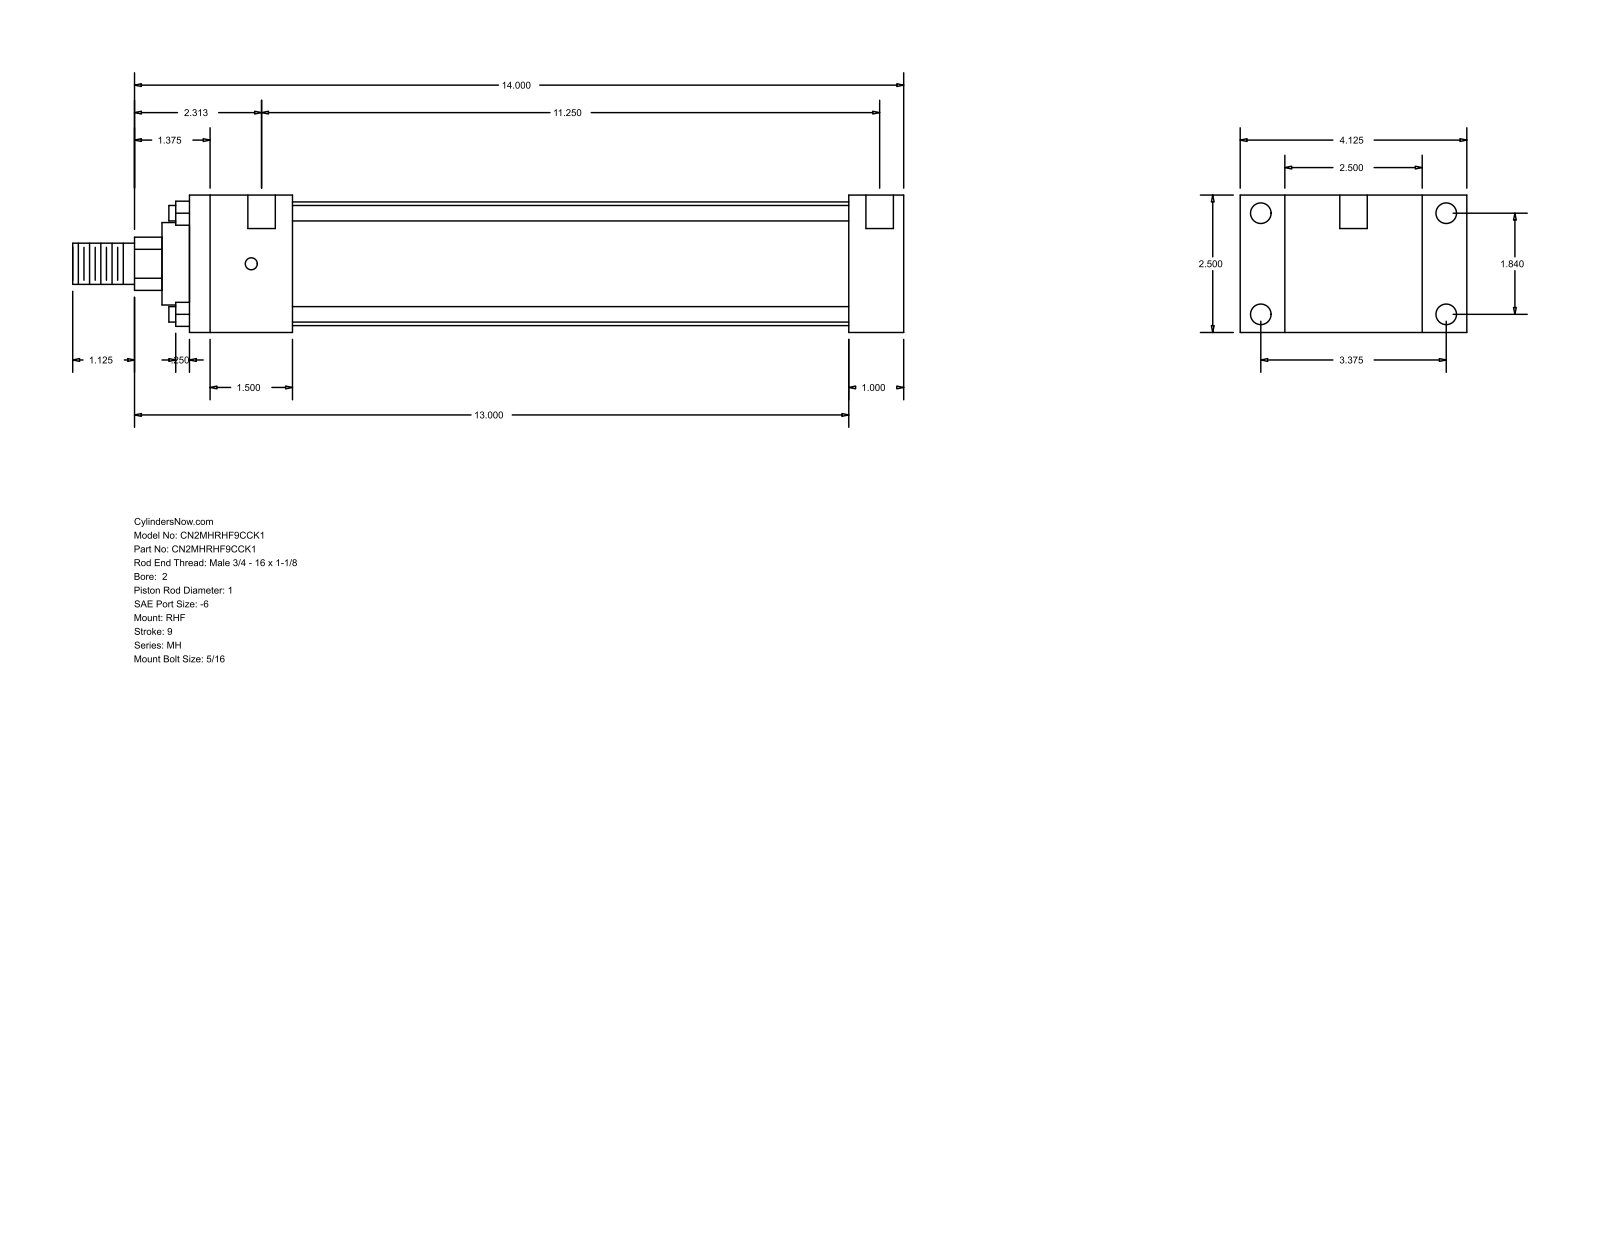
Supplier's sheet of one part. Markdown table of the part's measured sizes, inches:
| quantity | value |
| --- | --- |
| part name | MH_RHF__0200_1 |
| STEP written by | GSSL Pune (CONFIG_CONTROL_DESIGN) |
| units | inches |
| bodies | 0 solids, 88 faces (60 planar, 28 cylindrical, 0 other) |
| overall size | 15.125 × 4.125 × 2.5 |
| round holes (diameter × count) | 0.219 × 4, 0.375 × 4, 0.5 × 2 |
| round bosses / shafts (diameter × count) | 0.281 × 4, 2.25 × 1, 1.5 × 1, 1 × 1, 0.75 × 1 |
| partial cylindrical surfaces (radius × count) | 0.484 × 1 |
| main face-to-face distances | 2.5, 1, 0.813, 3.313, 13, 12, 4.125, 1.875, 10.125, 11.125 |
| hole center spacings | 1.84, 3.375, 3.844, 11.562, 0.125, 0.187, 11.25, 11.375 |
